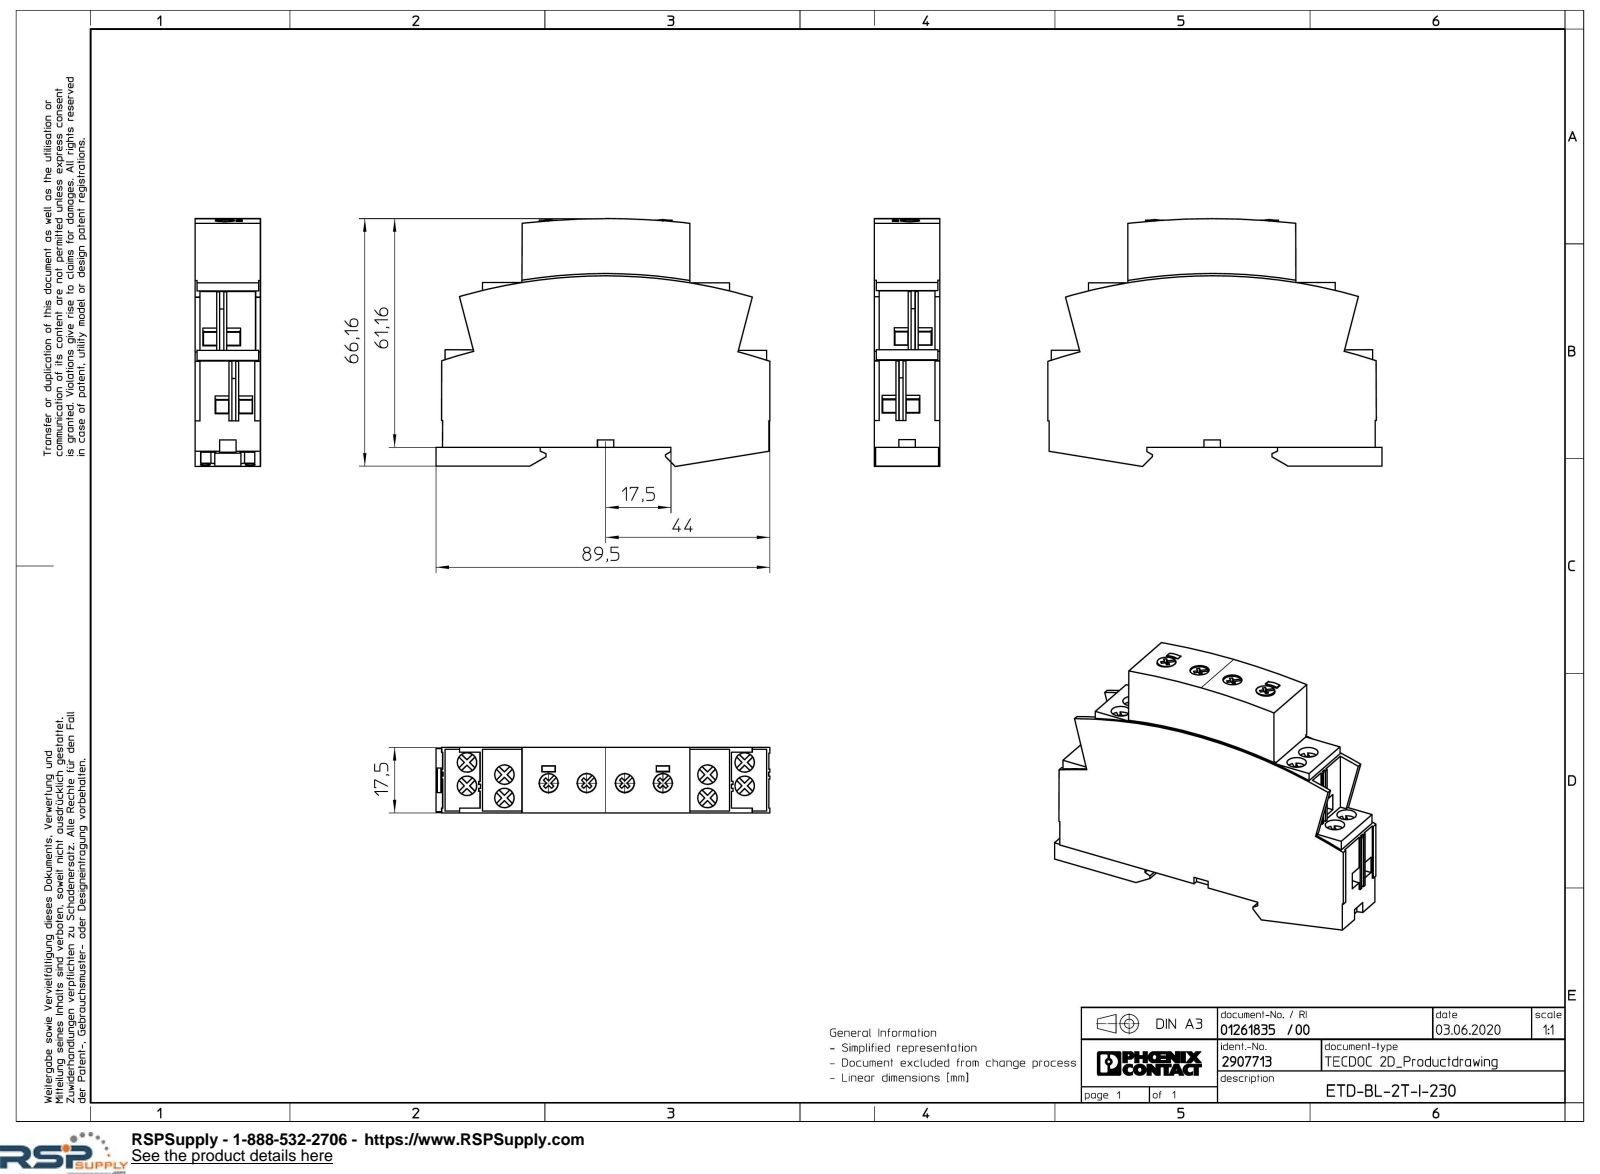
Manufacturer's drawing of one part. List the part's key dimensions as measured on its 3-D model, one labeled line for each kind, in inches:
Part name (STEP PRODUCT): EMD_BL_2T_I_400-select
STEP written by: Creo Elements/Direct Modeling 20.1A 29-Sep-2018 (C) Parametric Technology GmbH (AUTOMOTIVE_DESIGN)
Units: inches
Bodies: 1 solid, 467 faces (418 planar, 45 cylindrical, 4 other)
Overall size (bounding box): 3.524 × 2.609 × 0.689
Volume: 4.608 in³ · Surface area: 27.21 in²
Round holes (diameter × count): ⌀0.205 ×8, ⌀0.201 ×4, ⌀0.098 ×3, ⌀0.102 ×2
Round bosses / shafts (diameter × count): ⌀0.197 ×4
Partial cylindrical surfaces — rounded edges, fillets, slot ends (radius × count): R5.512 ×3, R0.246 ×2
Main face-to-face distances: 0.689, 0.197, 0.039, 0.051, 0.392, 0.677, 0.832, 0.832, 0.638, 0.657
Hole centre spacings: 0.246, 0.402, 0.197, 0.414, 0.414, 0.803, 2.142, 2.156
